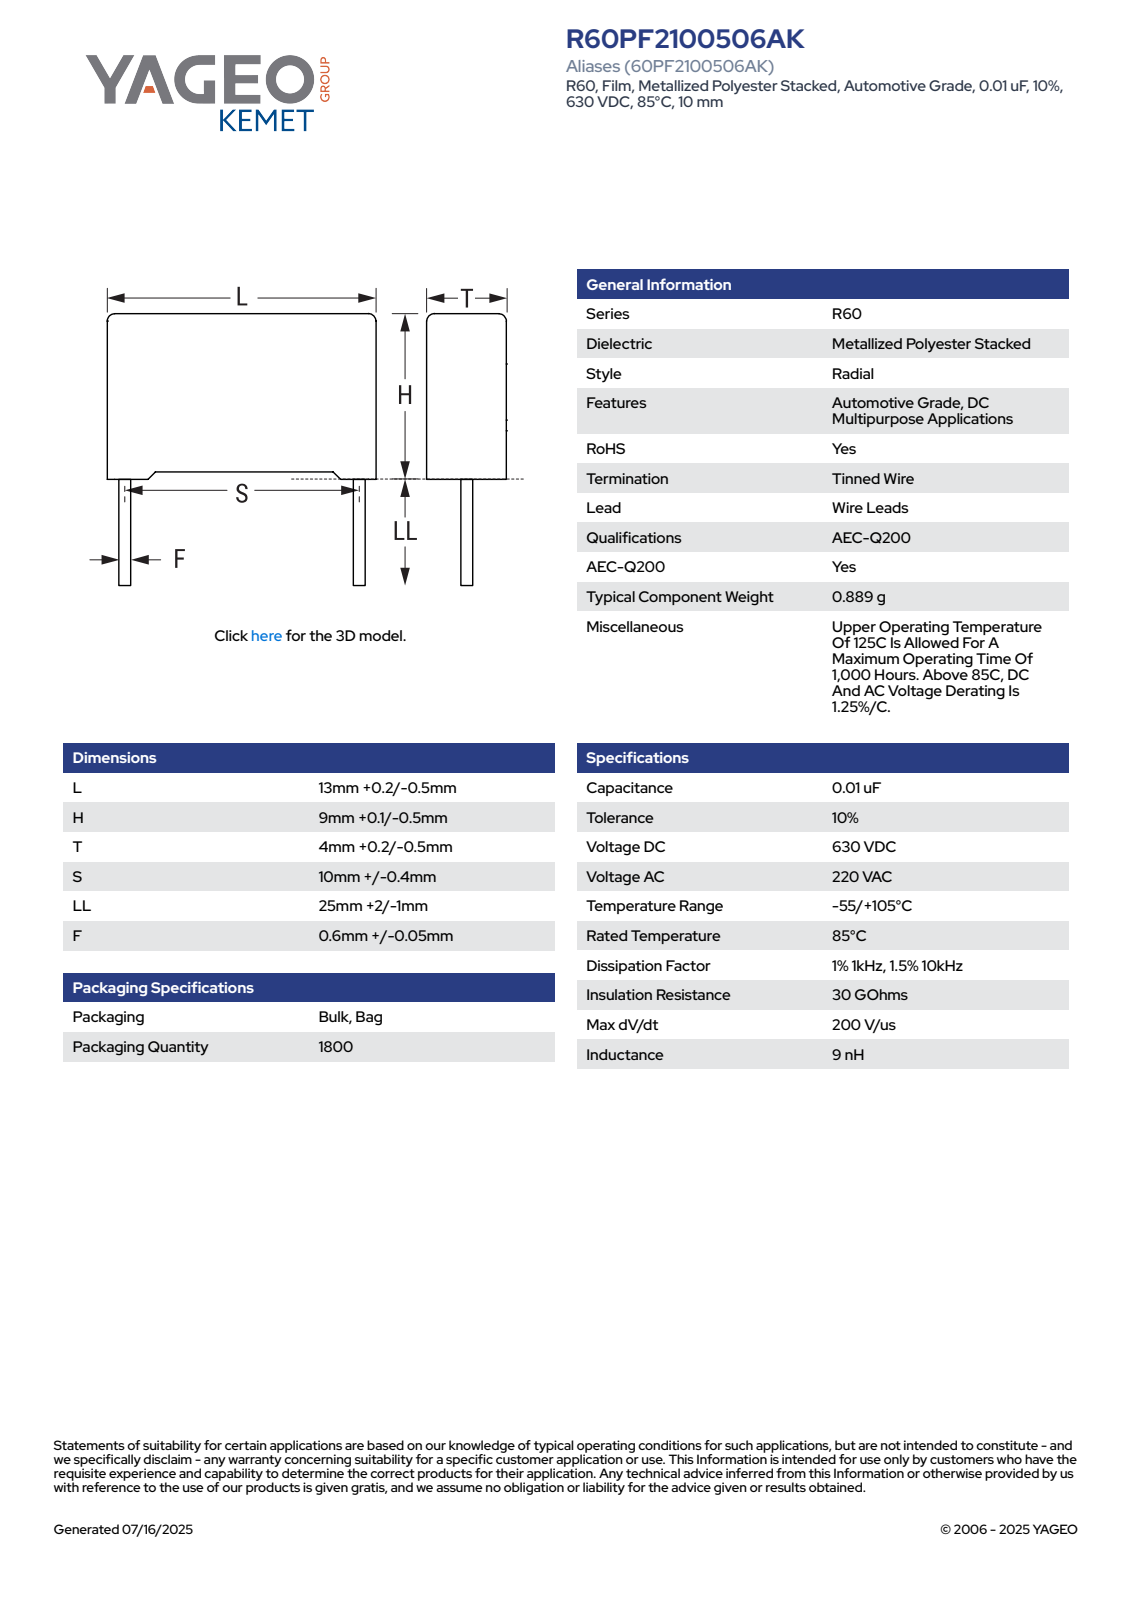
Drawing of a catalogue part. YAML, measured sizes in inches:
part_name: "CFR_RB2_13X9X4_L13.2H9.1T4.2S10LL27F0.65"
step_written_by: "SolidWorks 2021 (AUTOMOTIVE_DESIGN)"
units: inches
bodies: {solids: 4, faces: 85, planar: 77, cylindrical: 8, other: 0}
overall_size: [1.421, 0.52, 0.166]
volume: 0.03
surface_area: 0.871
round_bosses_or_shafts:
  - {diameter: 0.026, count: 2}
partial_cylinders:
  - {radius: 0.02, count: 4}
face_to_face_distances: [0.165, 0.329, 0.52, 0.017, 0.148, 0.03, 0.358, 0.131, 0.012, 0.346]
